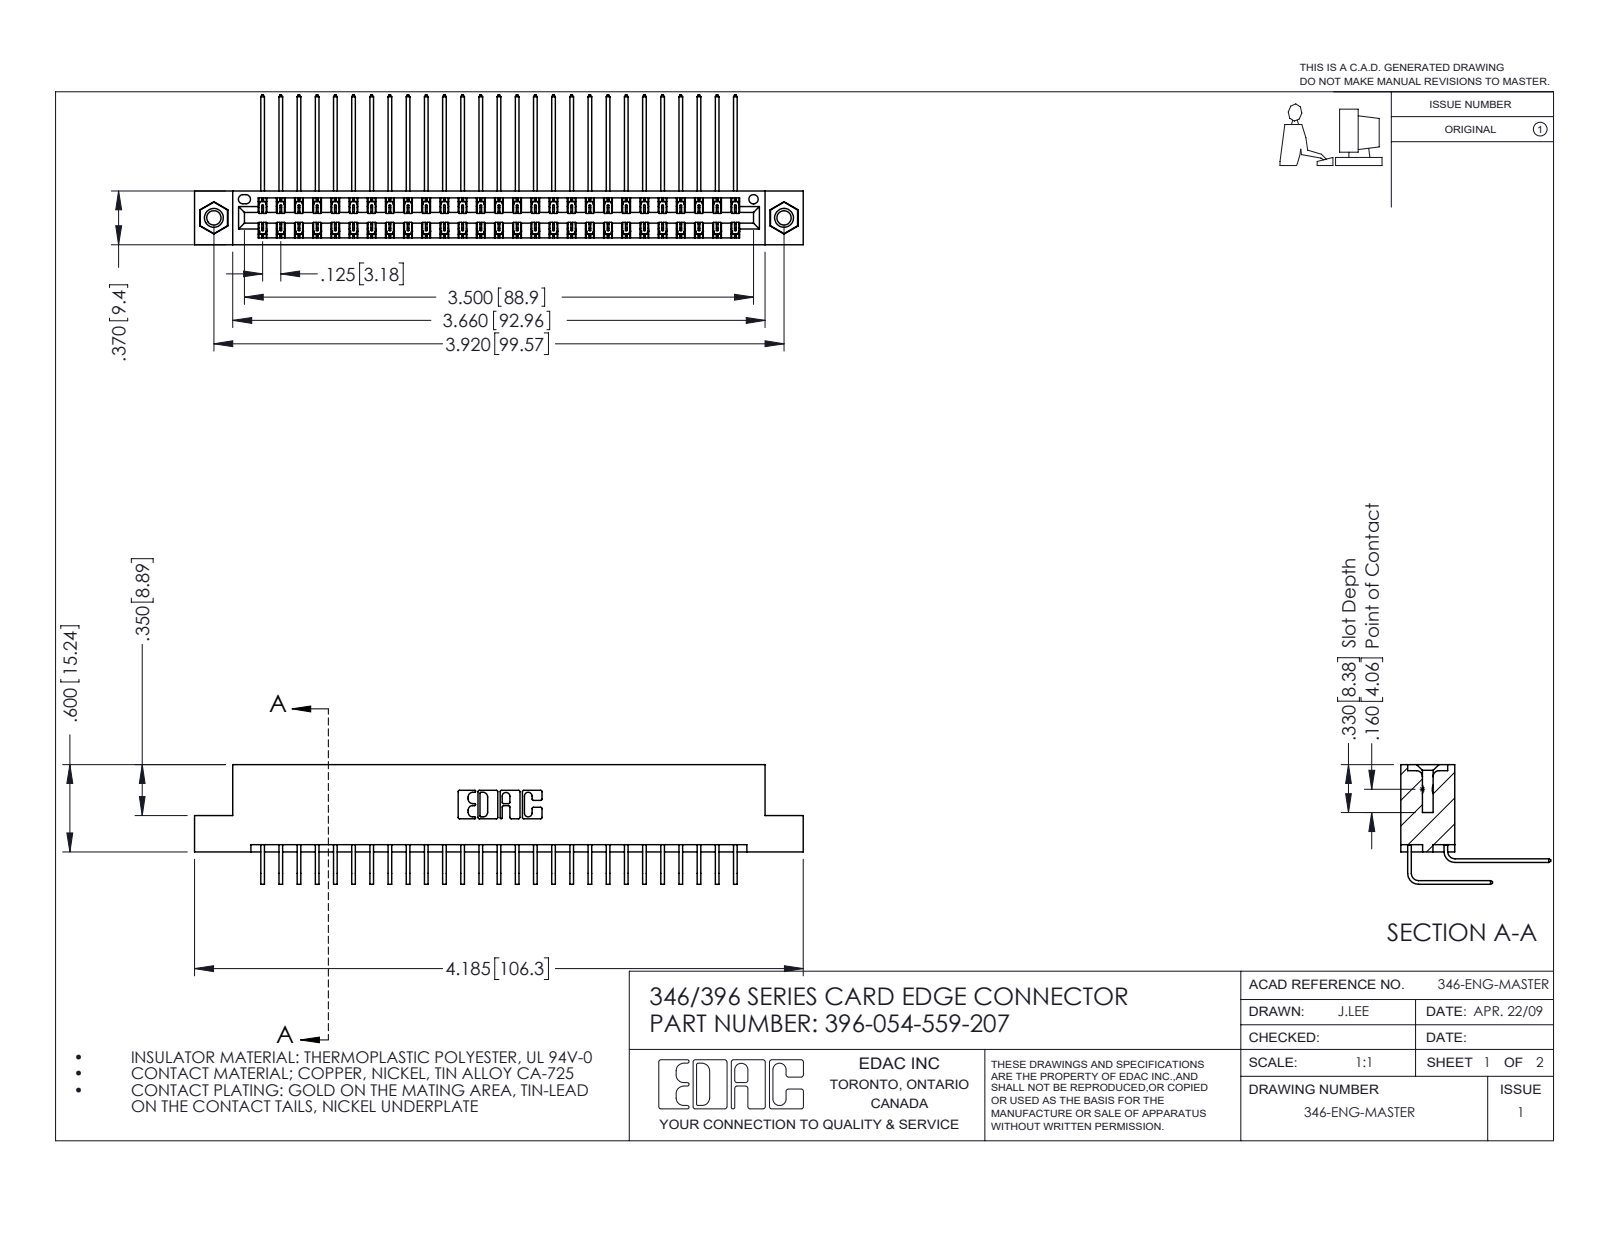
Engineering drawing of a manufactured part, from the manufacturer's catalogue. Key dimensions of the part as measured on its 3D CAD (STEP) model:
Part name (STEP PRODUCT): 345-292-001_558 559 Tail - 1; 345-250-001_345-250-005-103; 396-054-559-207; 345-292-001_559 Tail - 2 (+1 more)
STEP written by: SolidWorks 2016 (CONFIG_CONTROL_DESIGN)
Units: inches
Bodies: 57 solids, 3098 faces (2106 planar, 976 cylindrical, 16 other)
Overall size (bounding box): 4.185 × 1.03 × 0.823
Volume: 0.644 in³ · Surface area: 24.47 in²
Round holes (diameter × count): ⌀0.098 ×2, ⌀0.125 ×2, ⌀0.156 ×2, ⌀0.064 ×1
Round bosses / shafts (diameter × count): ⌀0.155 ×2
Partial cylindrical surfaces — rounded edges, fillets, slot ends (radius × count): R0.006 ×81, R0.01 ×22, R0.007 ×6, R0.031 ×6, R0.026 ×3, R0.014 ×2, R0.022 ×2, R0.024 ×2
Main face-to-face distances: 0.048, 0.322, 0.025, 0.25, 0.37, 0.072, 0.298, 0.275, 0.148, 0.222
Hole centre spacings: 0.246, 3.712, 3.92
